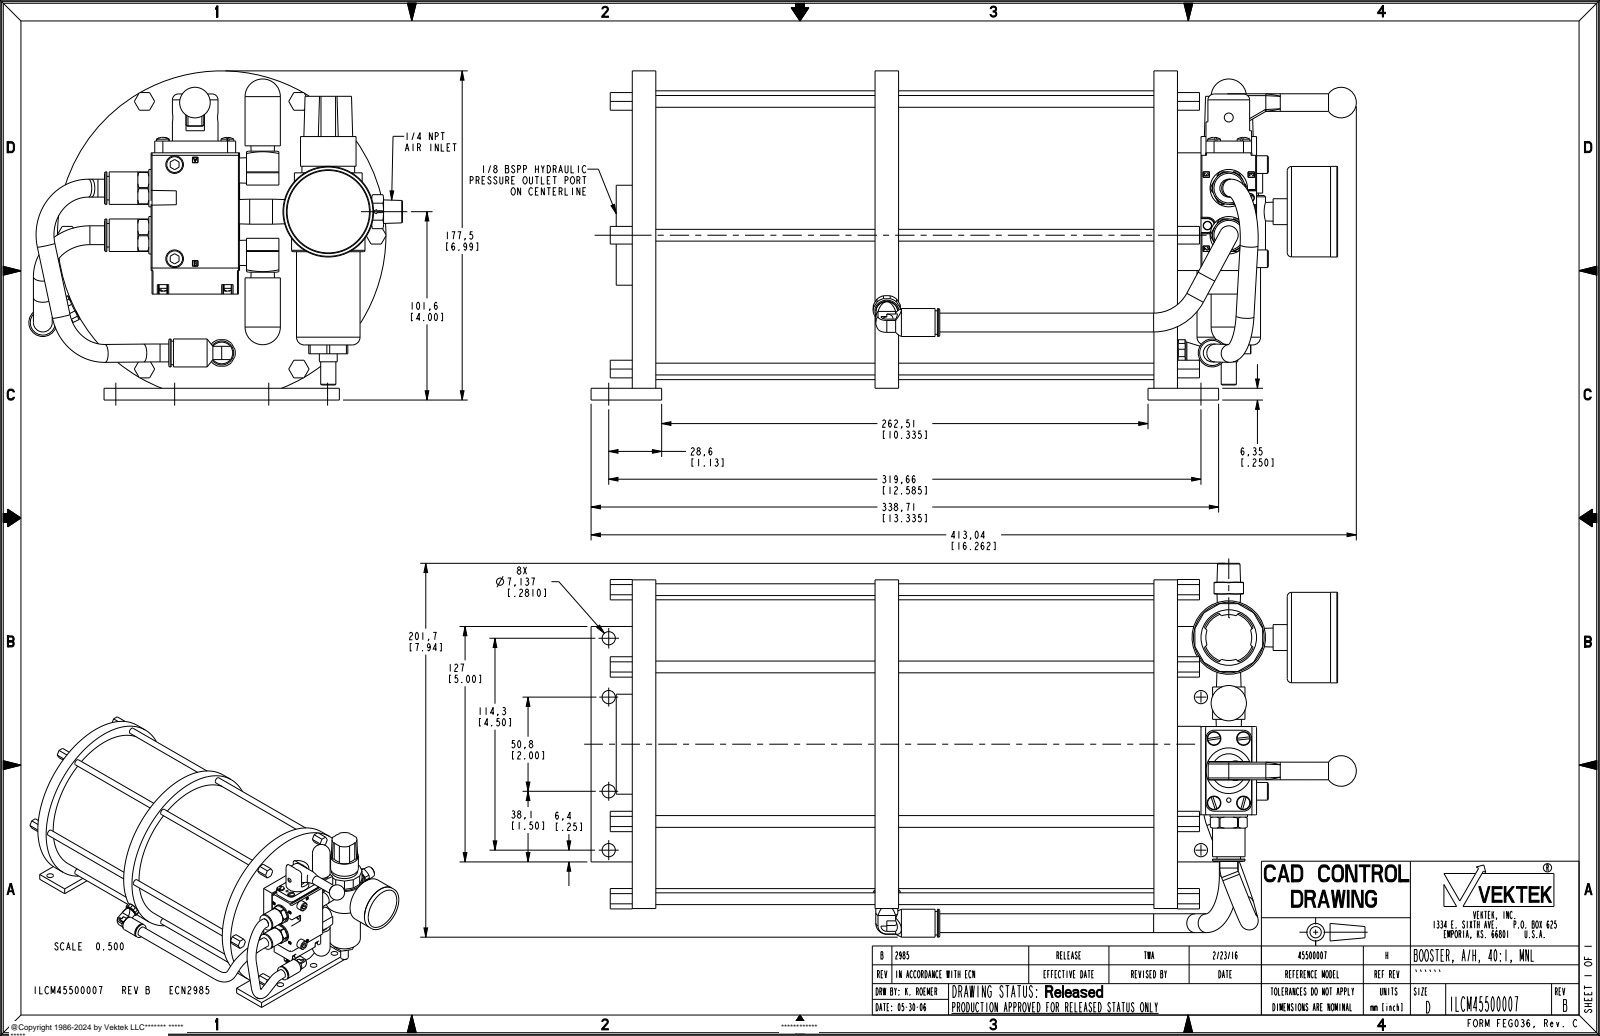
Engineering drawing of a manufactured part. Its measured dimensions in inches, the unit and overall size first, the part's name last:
Units: inches
Overall size (bounding box): 16.261 × 7.939 × 6.99
Round holes (diameter × count): ⌀0.281 ×12, ⌀0.201 ×4, ⌀0.5 ×3, ⌀0.213 ×2, ⌀0.262 ×2, ⌀0.54 ×2, ⌀0.69 ×2, ⌀0.794 ×2, ⌀0.094 ×1, ⌀0.098 ×1, ⌀0.145 ×1, ⌀0.19 ×1
Round bosses / shafts (diameter × count): ⌀0.25 ×12, ⌀0.38 ×6, ⌀0.4 ×4, ⌀0.375 ×4, ⌀0.272 ×4, ⌀0.46 ×3, ⌀0.594 ×2, ⌀0.5 ×2
Partial cylindrical surfaces — rounded edges, fillets, slot ends (radius × count): R0.039 ×19, R0.02 ×16, R0.06 ×6, R0.02 ×4, R0.13 ×4, R0.146 ×4, R0.172 ×4, R0.235 ×4
Main face-to-face distances: 11.585, 0.5, 11.085, 5.159, 5.926, 0.25, 6.426, 5.659, 4.659, 10.585
Hole centre spacings: 2, 0.75, 1.25, 1.458, 2.136, 3.25, 3.335, 11.835
Volume: 365 in³ · Surface area: 583.8 in²
Bodies: 1 solid, 1189 faces (552 planar, 330 cylindrical, 307 other)
Part name (STEP PRODUCT): ILCM45500007
STEP written by: PRO/ENGINEER BY PARAMETRIC TECHNOLOGY CORPORATION, 2013320 (CONFIG_CONTROL_DESIGN)
